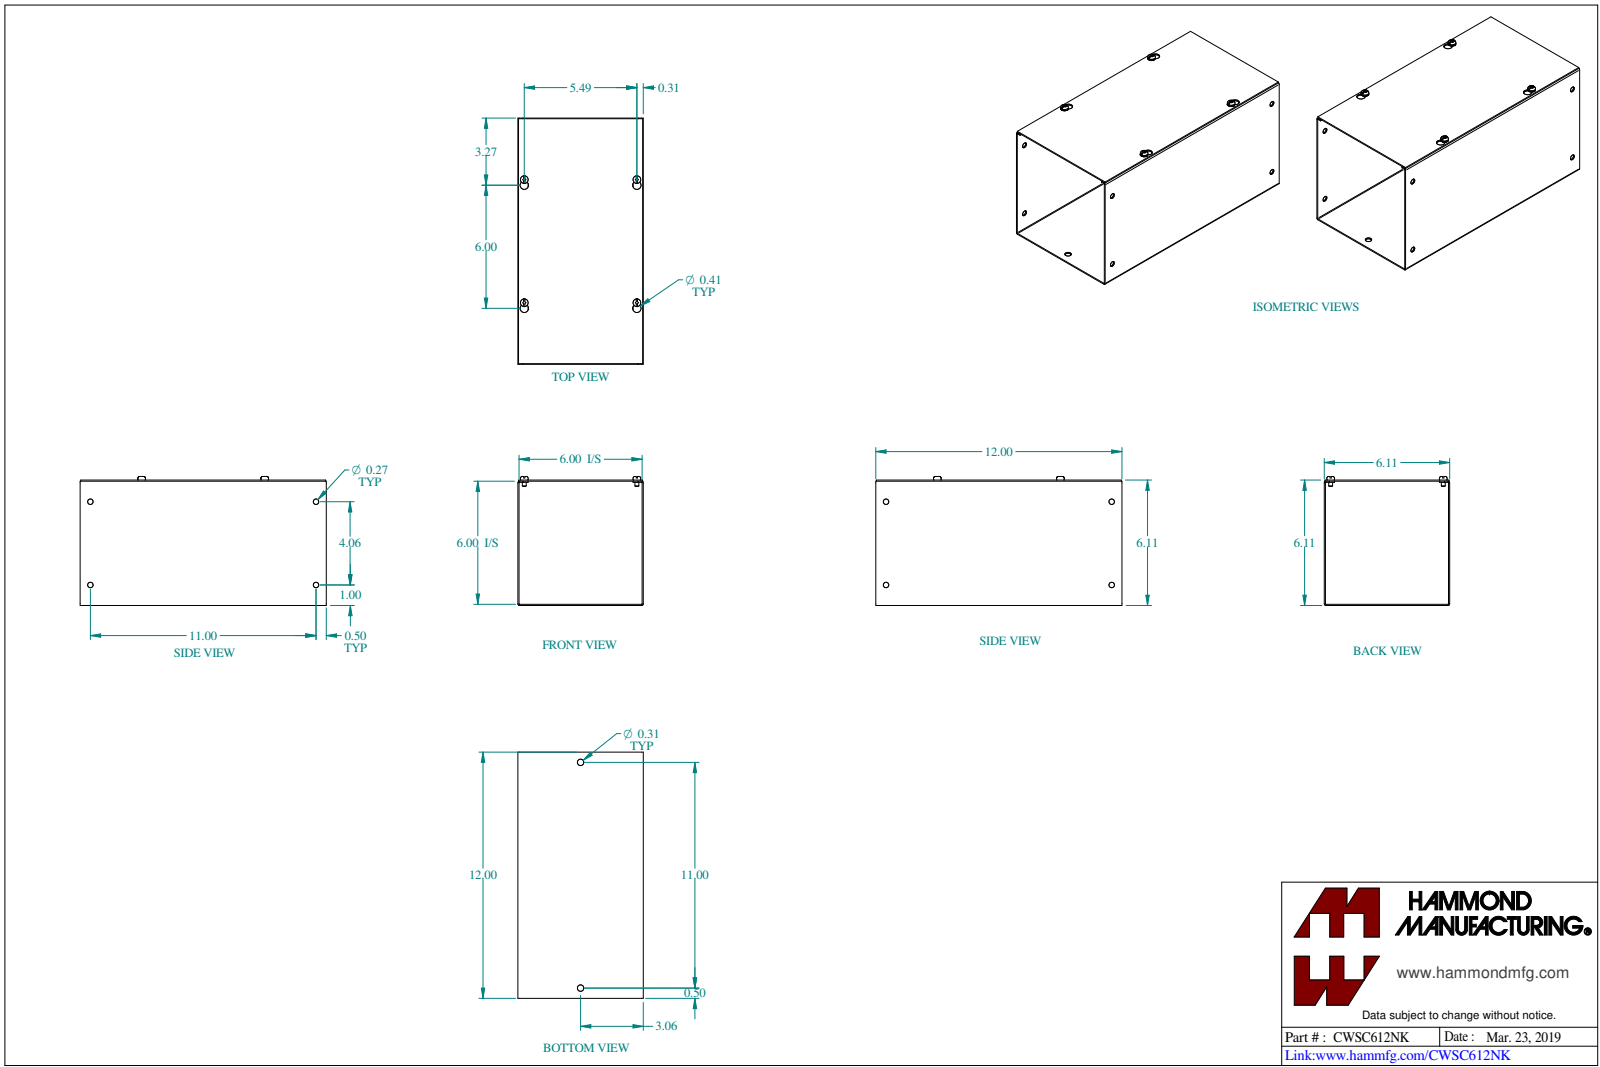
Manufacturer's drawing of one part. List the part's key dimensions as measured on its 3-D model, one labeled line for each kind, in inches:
Part name (STEP PRODUCT): CWSC612NK
STEP written by: SolidWorks 2023 (CONFIG_CONTROL_DESIGN)
Units: inches
Bodies: 6 solids, 180 faces (88 planar, 68 cylindrical, 24 other)
Overall size (bounding box): 12 × 6.289 × 6.114
Volume: 17 in³ · Surface area: 602.2 in²
Round holes (diameter × count): ⌀0.177 ×4, ⌀0.266 ×4, ⌀0.313 ×2
Round bosses / shafts (diameter × count): ⌀0.375 ×4, ⌀0.19 ×4
Partial cylindrical surfaces — rounded edges, fillets, slot ends (radius × count): R0.029 ×4, R0.086 ×4, R0.125 ×4, R0.203 ×4
Main face-to-face distances: 0.057, 6.057, 6, 6.114, 5.943, 0.114, 0.031, 6.083, 0.026, 6.026
Hole centre spacings: 3.713, 8.932, 11, 4.057, 5.489, 6, 8.132, 11.724
